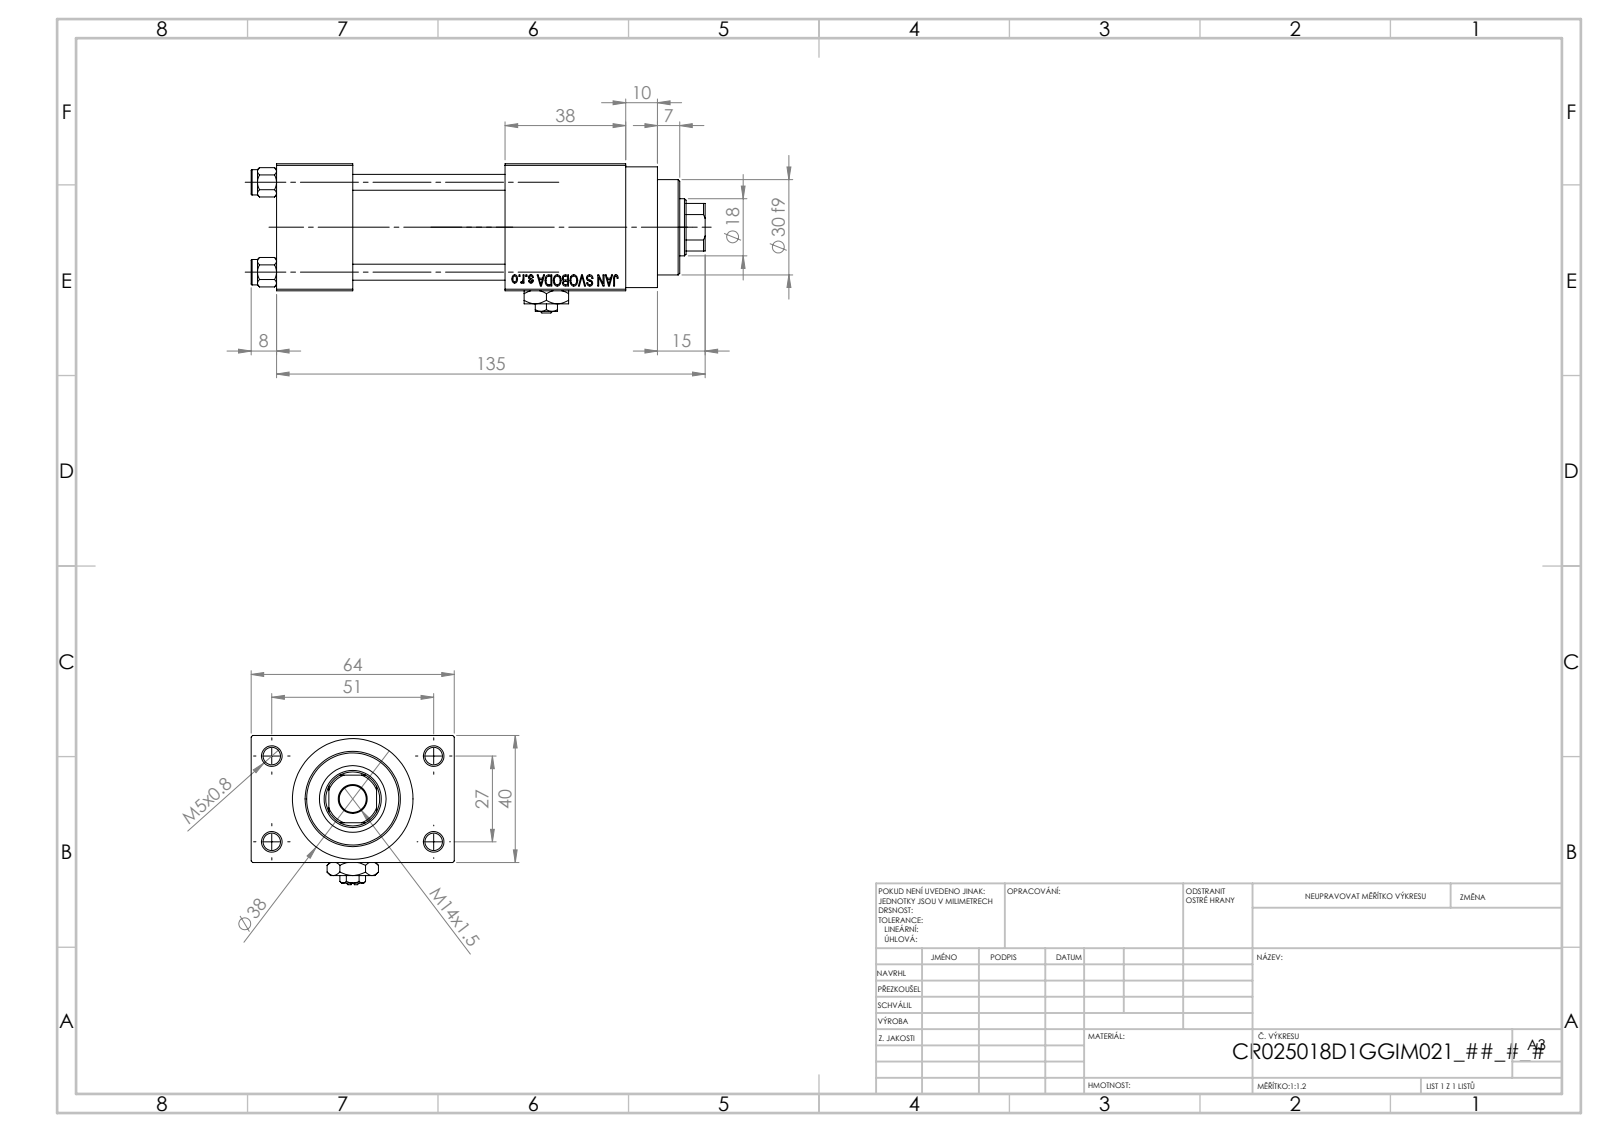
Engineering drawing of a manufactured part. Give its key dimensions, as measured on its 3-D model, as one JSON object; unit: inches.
{"part_name": "V215CR_D_TYCINKA; V215_VC_A; V215CR_D_Body; NUT_M5_D (+2 more)", "step_written_by": "SolidWorks 2019 (CONFIG_CONTROL_DESIGN)", "units": "inches", "bodies": {"solids": 12, "faces": 1147, "planar": 518, "cylindrical": 91, "other": 538}, "overall_size": [5.63, 2.52, 1.85], "volume_in3": 11.07, "surface_area_in2": 100.9, "round_holes": [[0.197, 4], [0.217, 4], [0.787, 3], [0.276, 2], [0.518, 2], [0.335, 1], [0.709, 1], [0.827, 1], [0.984, 1], [1.181, 1]], "round_bosses_or_shafts": [[0.315, 4], [1.496, 1], [1.22, 1]], "partial_cylinders_radius": [[0.335, 1]], "face_to_face_distances": [1.575, 1.89, 0.472, 2.047, 0.945, 2.835, 2.52, 1.496, 3.386, 4.331], "hole_center_spacings": [0.448, 0.788, 1.114, 1.136, 1.177, 1.561, 1.903, 1.063]}
